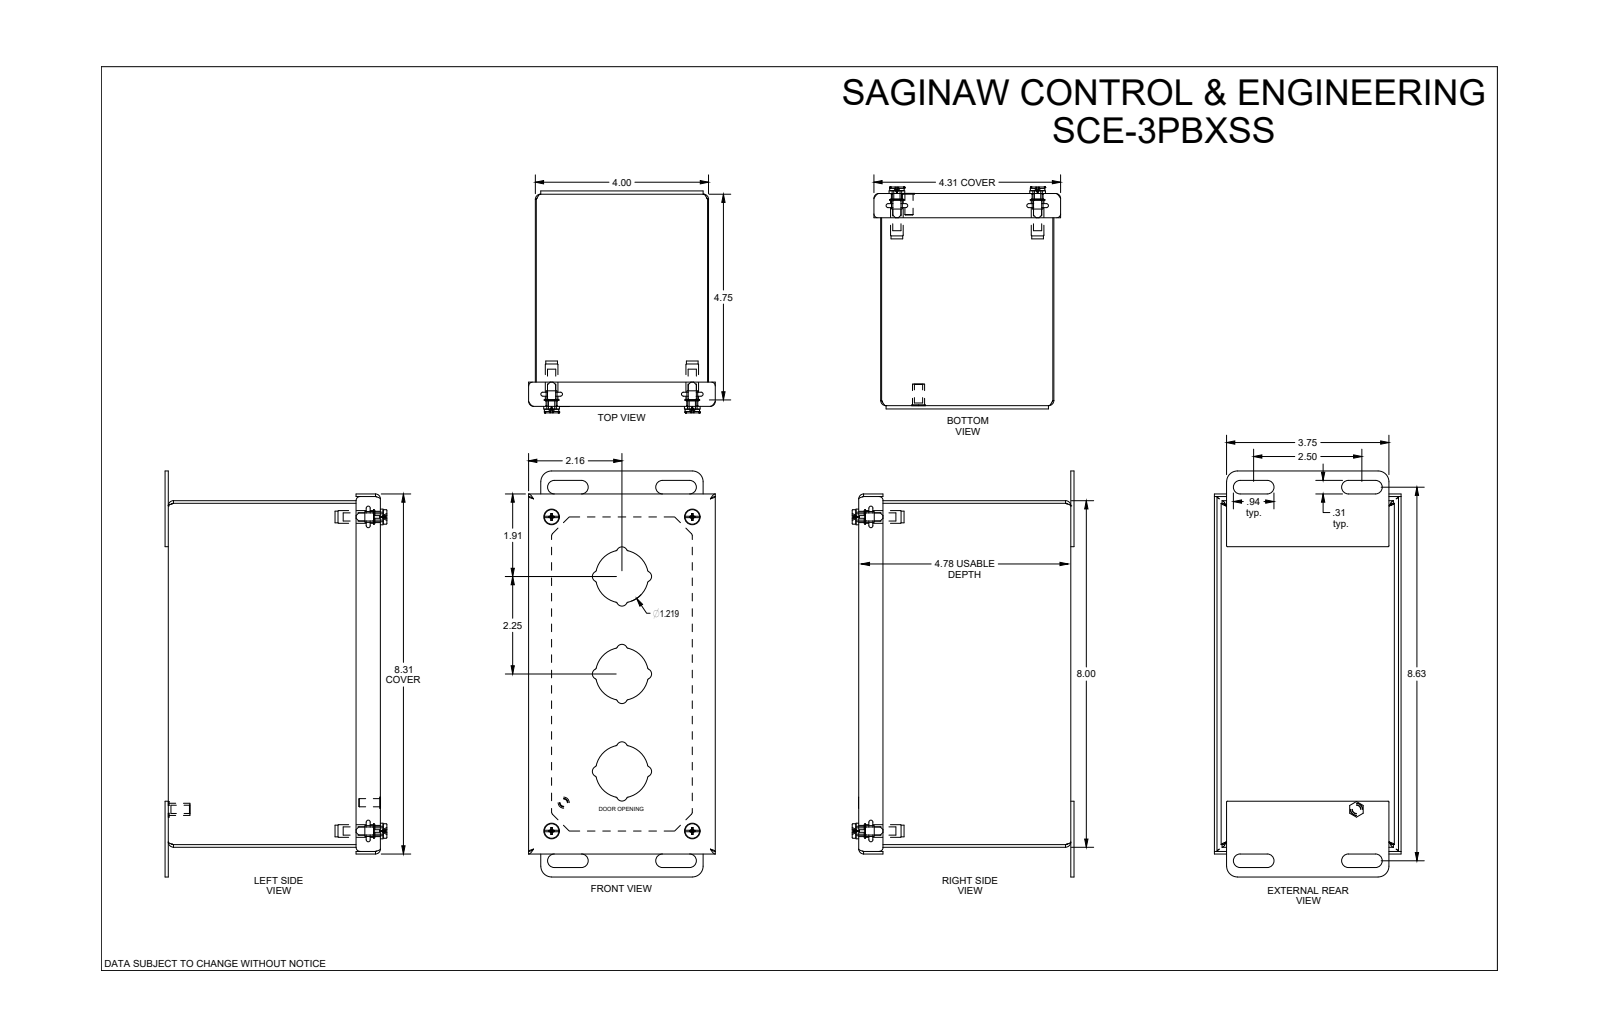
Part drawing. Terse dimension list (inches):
name: SCE-3PBX
written by: SolidWorks 2021 (AUTOMOTIVE_DESIGN)
unit: in
bodies: 14 solids, 450 faces (159 planar, 150 cylindrical, 141 other)
size: 9.375 × 5.124 × 4.313
volume: 13.14 in³; area: 435.2 in²
holes: 4× ⌀0.22, 4× ⌀0.266, 4× ⌀0.317
bosses: 5× ⌀0.188, 4× ⌀0.362, 4× ⌀0.334, 4× ⌀0.26, 4× ⌀0.146, 1× ⌀0.256
rounds: 28× R0.06, 24× R0.04, 12× R0.125, 8× R0.015, 8× R0.115, 8× R0.156, 8× R0.245, 4× R0.02
face distances: 0.06, 3.94, 4.838, 4, 3.88, 7.94, 4.898, 4.778, 8, 7.88
hole spacings: 3.25, 7.25, 7.945
